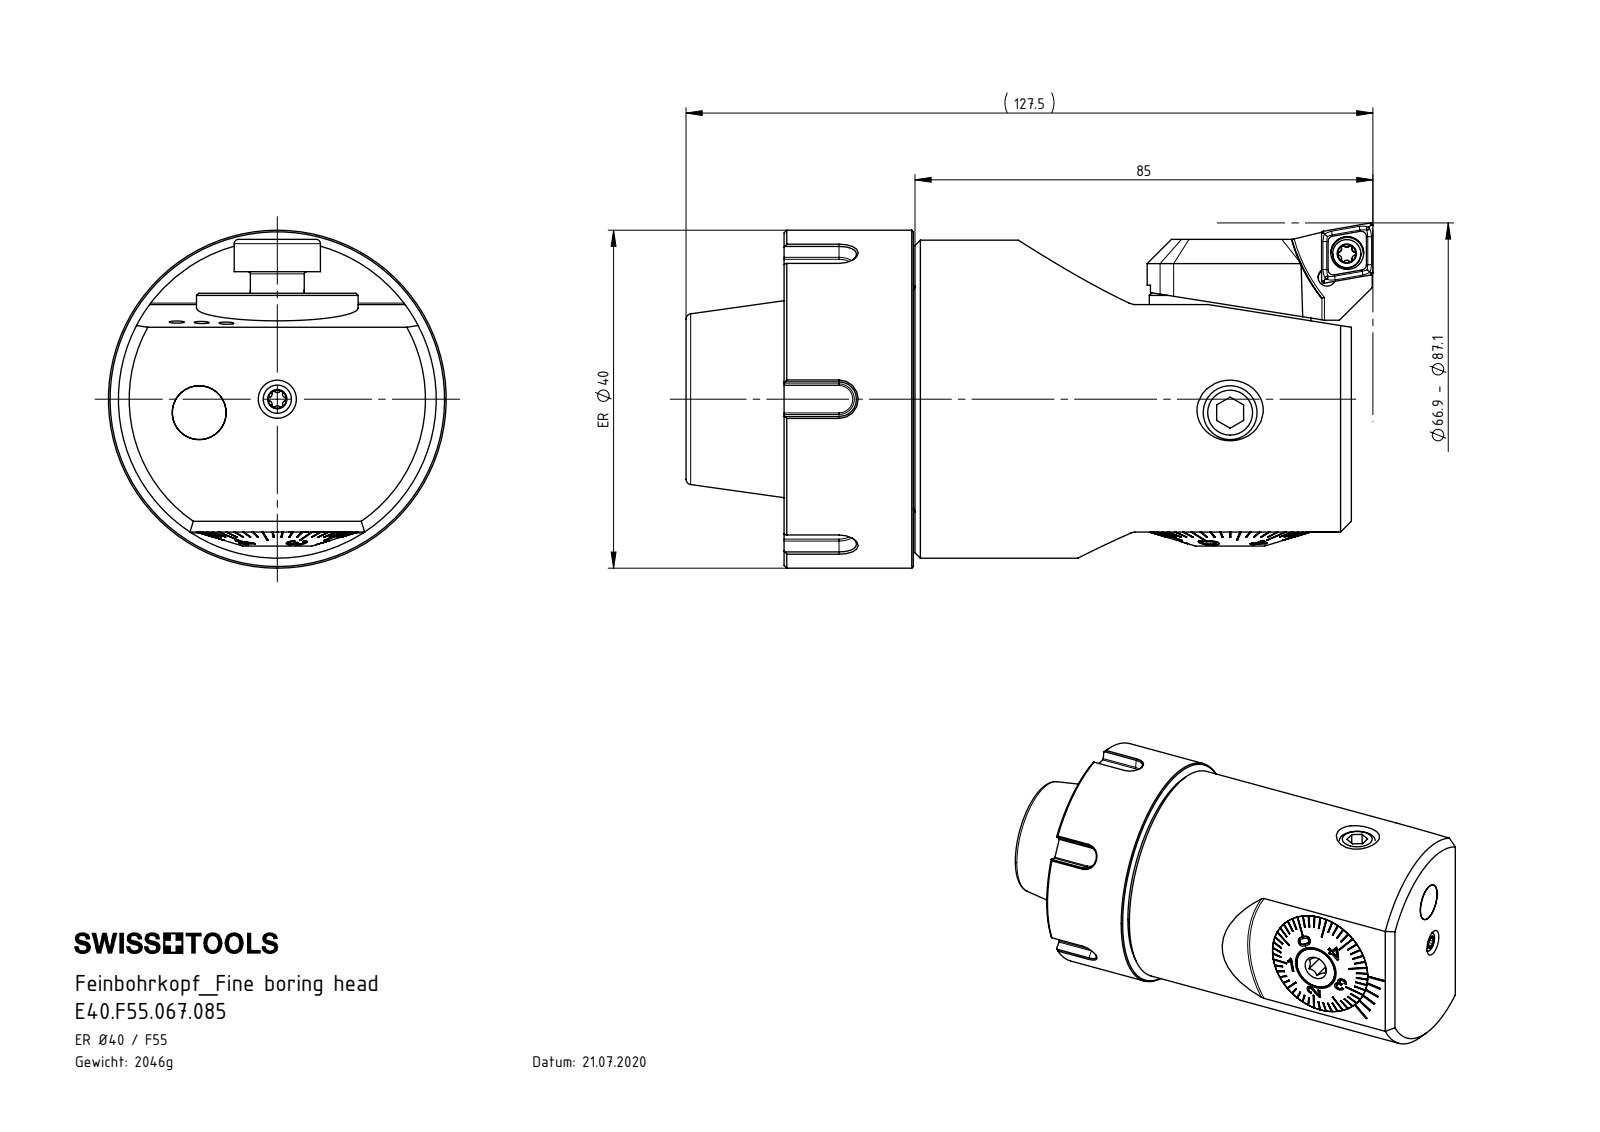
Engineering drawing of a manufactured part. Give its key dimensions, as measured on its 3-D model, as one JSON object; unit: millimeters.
{"part_name": "DIN 7984 - M10 x 16; A55-BG2.012.006_B; E40.F55.AA4.085; WCB-ER2.001.009_A (+8 more)", "step_written_by": "SolidWorks 2017 (AUTOMOTIVE_DESIGN)", "units": "millimeters", "bodies": {"solids": 15, "faces": 639, "planar": 336, "cylindrical": 98, "other": 205}, "overall_size": [123.5, 62.7, 62.7], "volume_mm3": 262931, "surface_area_mm2": 61456, "round_holes": [[2.5, 3], [4.2, 3], [3.3, 2], [8.5, 2], [5, 1], [8, 1], [10, 1], [10.2, 1], [11.4, 1], [12, 1], [12.4, 1], [13, 1]], "round_bosses_or_shafts": [[10, 2], [62.7, 1], [59, 1], [40, 1], [37.5, 1], [30, 1], [29.98, 1], [29.9, 1]], "partial_cylinders_radius": [[0.3, 12], [0.34, 6], [0.59, 6], [2.5, 6], [2, 4], [3.2, 3], [0.5, 2], [1, 1]], "face_to_face_distances": [81.3, 42.2, 81, 24, 24.3, 105.3, 35.7, 2.7, 2.5, 6.5], "hole_center_spacings": [14.71, 17.33]}
